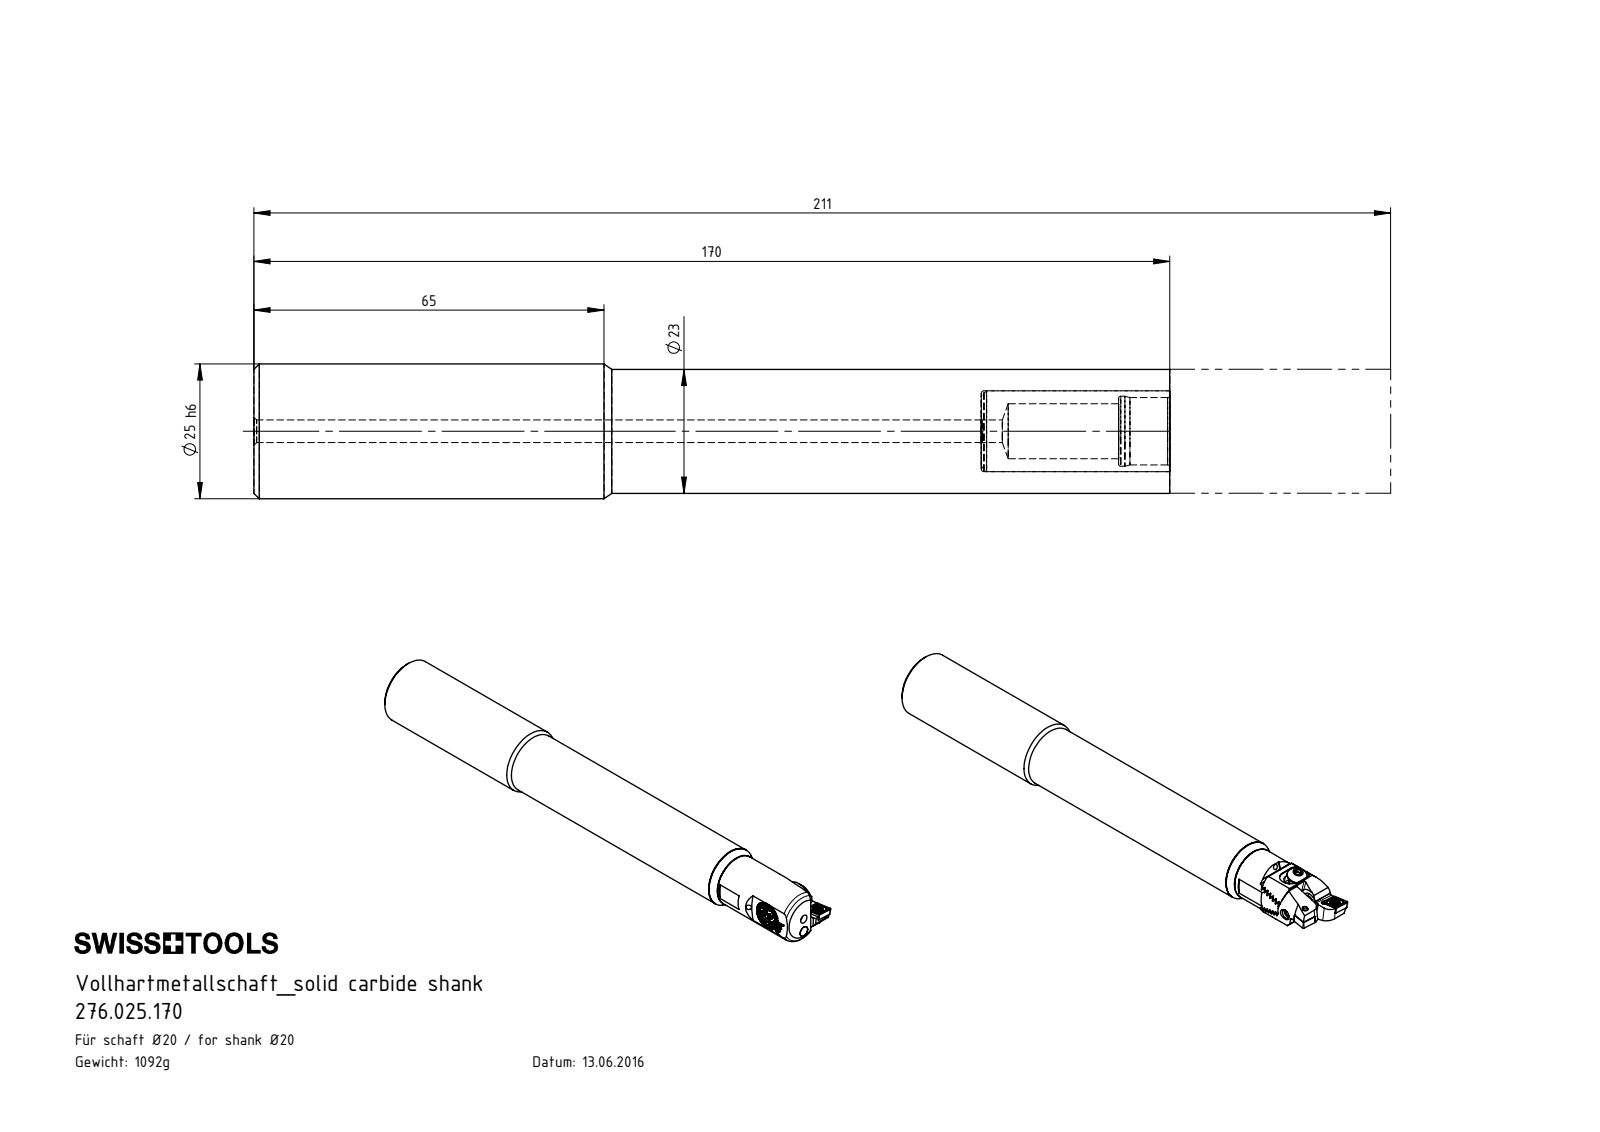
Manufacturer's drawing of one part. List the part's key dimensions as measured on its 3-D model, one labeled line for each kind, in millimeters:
Part name (STEP PRODUCT): U25-HP4.023.170_A; HP4-ER1.015.035_A; U25.HP4.023.170
STEP written by: SolidWorks 2017 (AUTOMOTIVE_DESIGN)
Units: millimetres
Bodies: 2 solids, 25 faces (6 planar, 9 cylindrical, 10 other)
Overall size (bounding box): 170 × 25 × 25
Volume: 70 696 mm³ · Surface area: 19 999 mm²
Round holes (diameter × count): ⌀4.2 ×1, ⌀10.2 ×1, ⌀12.5 ×1, ⌀13 ×1, ⌀15 ×1
Round bosses / shafts (diameter × count): ⌀25 ×1, ⌀23 ×1
Main face-to-face distances: 170, 135, 35, 160.5, 25.5, 9.5
